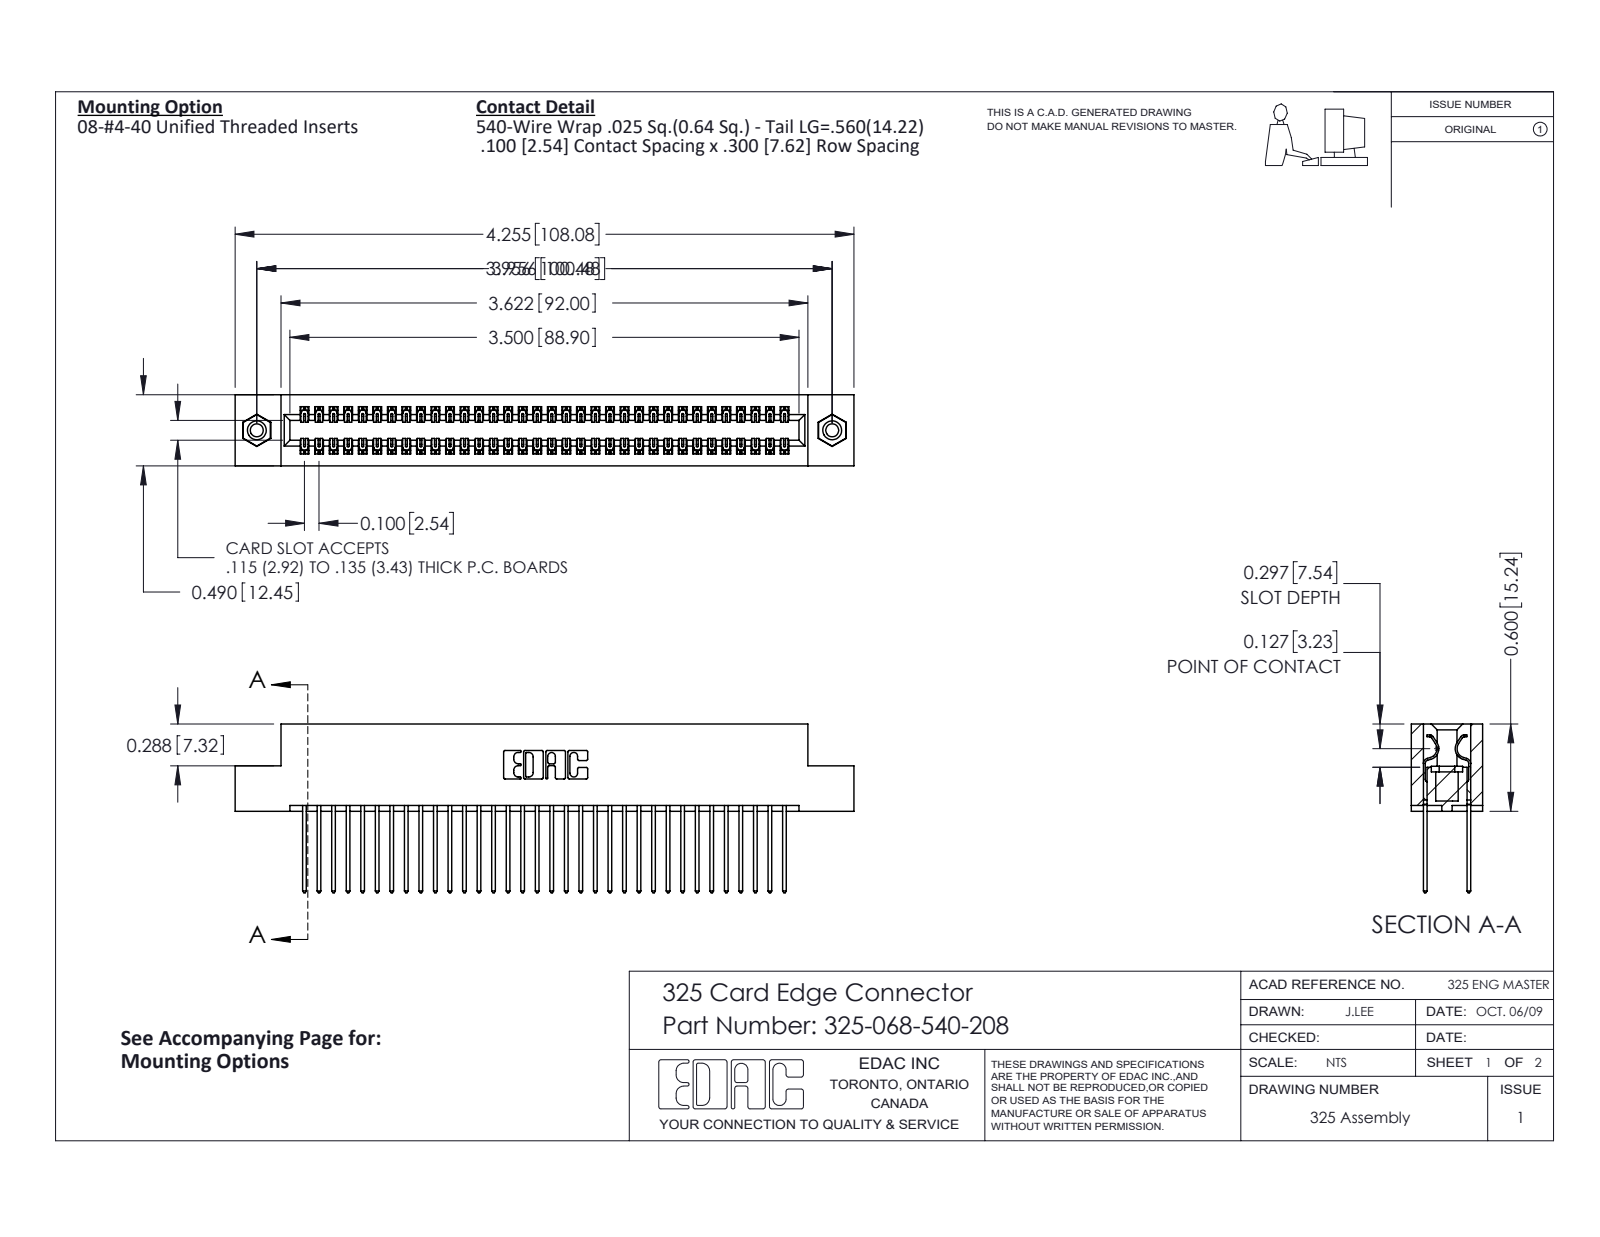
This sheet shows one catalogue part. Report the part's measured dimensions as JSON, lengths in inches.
{"part_name": "325-068-540-208; 325-292-001_325-293-140; 325 Part_TI; 345-250-001_345-250-003-102", "step_written_by": "SolidWorks 2016 (CONFIG_CONTROL_DESIGN)", "units": "inches", "bodies": {"solids": 71, "faces": 3710, "planar": 2550, "cylindrical": 1144, "other": 16}, "overall_size": [4.255, 1.16, 0.49], "volume_in3": 0.862, "surface_area_in2": 28.14, "round_holes": [[0.089, 2], [0.125, 2], [0.16, 2]], "round_bosses_or_shafts": [[0.155, 2]], "partial_cylinders_radius": [[0.006, 102], [0.01, 68], [0.01, 22], [0.007, 6], [0.031, 6], [0.026, 3], [0.014, 2], [0.022, 2]], "face_to_face_distances": [0.083, 0.407, 0.3, 0.107, 0.383, 0.025, 0.49, 0.325, 0.275, 0.04], "hole_center_spacings": [3.956]}
